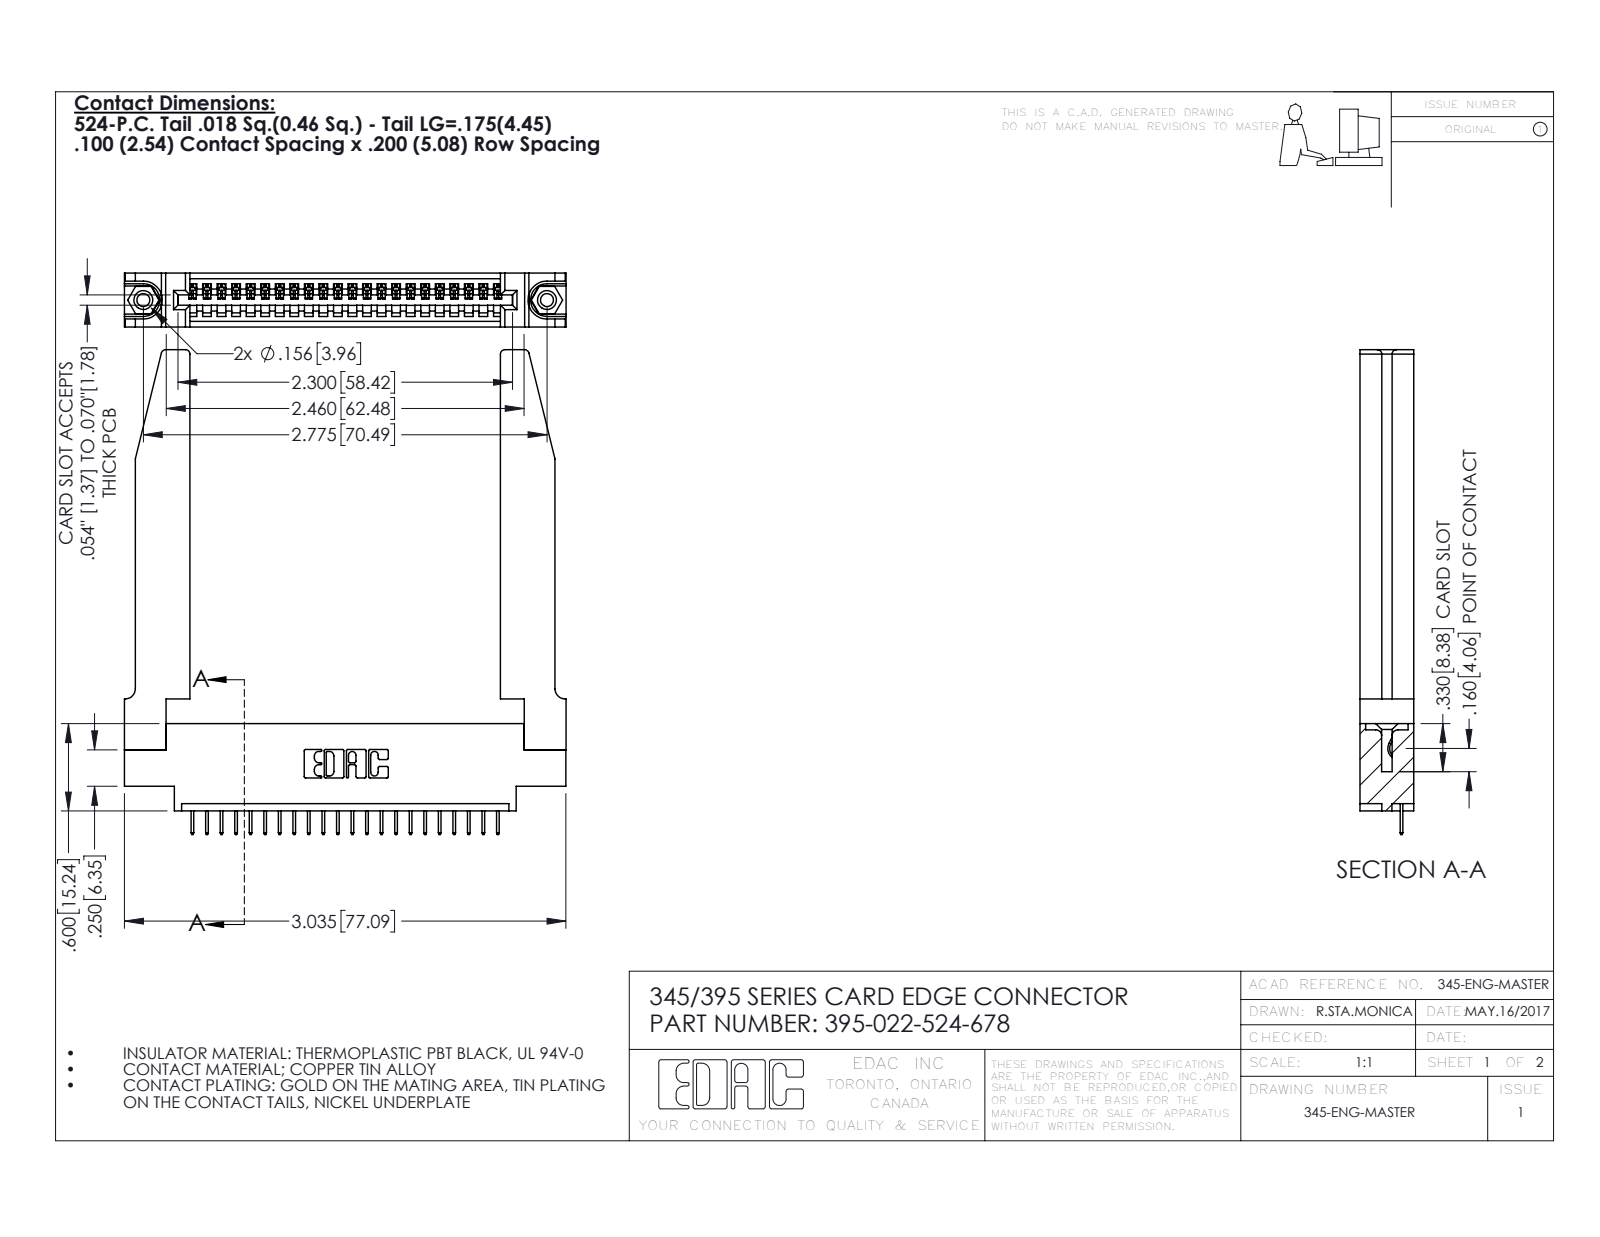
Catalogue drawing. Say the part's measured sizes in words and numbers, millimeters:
The part is named "345-220-078_345-220-078; 395-022-524-678; 345-250-001_345-250-001-102; 345-292-001_345-293-124 (+1 more)". Its 3-D file was written by "SolidWorks 2016 (CONFIG_CONTROL_DESIGN)". It is 27 solids with 1728 faces: 1238 planar, 438 cylindrical and 52 other. Overall it measures 84.6 by 77.1 by 9.4 millimeters. Its volume is 14 700 cubic millimeters and its surface area 15 670 square millimeters. Round holes: 2 of diameter 2.3, 2 of diameter 3.2, 2 of diameter 4, 1 of diameter 1.6. Round bosses or shafts: 2 of diameter 3.9. Partial cylindrical surfaces (rounded edges, fillets, slot ends): 44 of radius 0.2, 22 of radius 0.3, 8 of radius 0.8, 6 of radius 0.2, 6 of radius 0.8, 3 of radius 0.7, 2 of radius 0.8, 2 of radius 1. The main face-to-face distances are 9.4, 1.8, 7.6, 3.8, 3.8, 2.5, 6.9, 0.6, 5.1, 3.1. The hole center spacings are 6.9, 64.5, 70.5.
